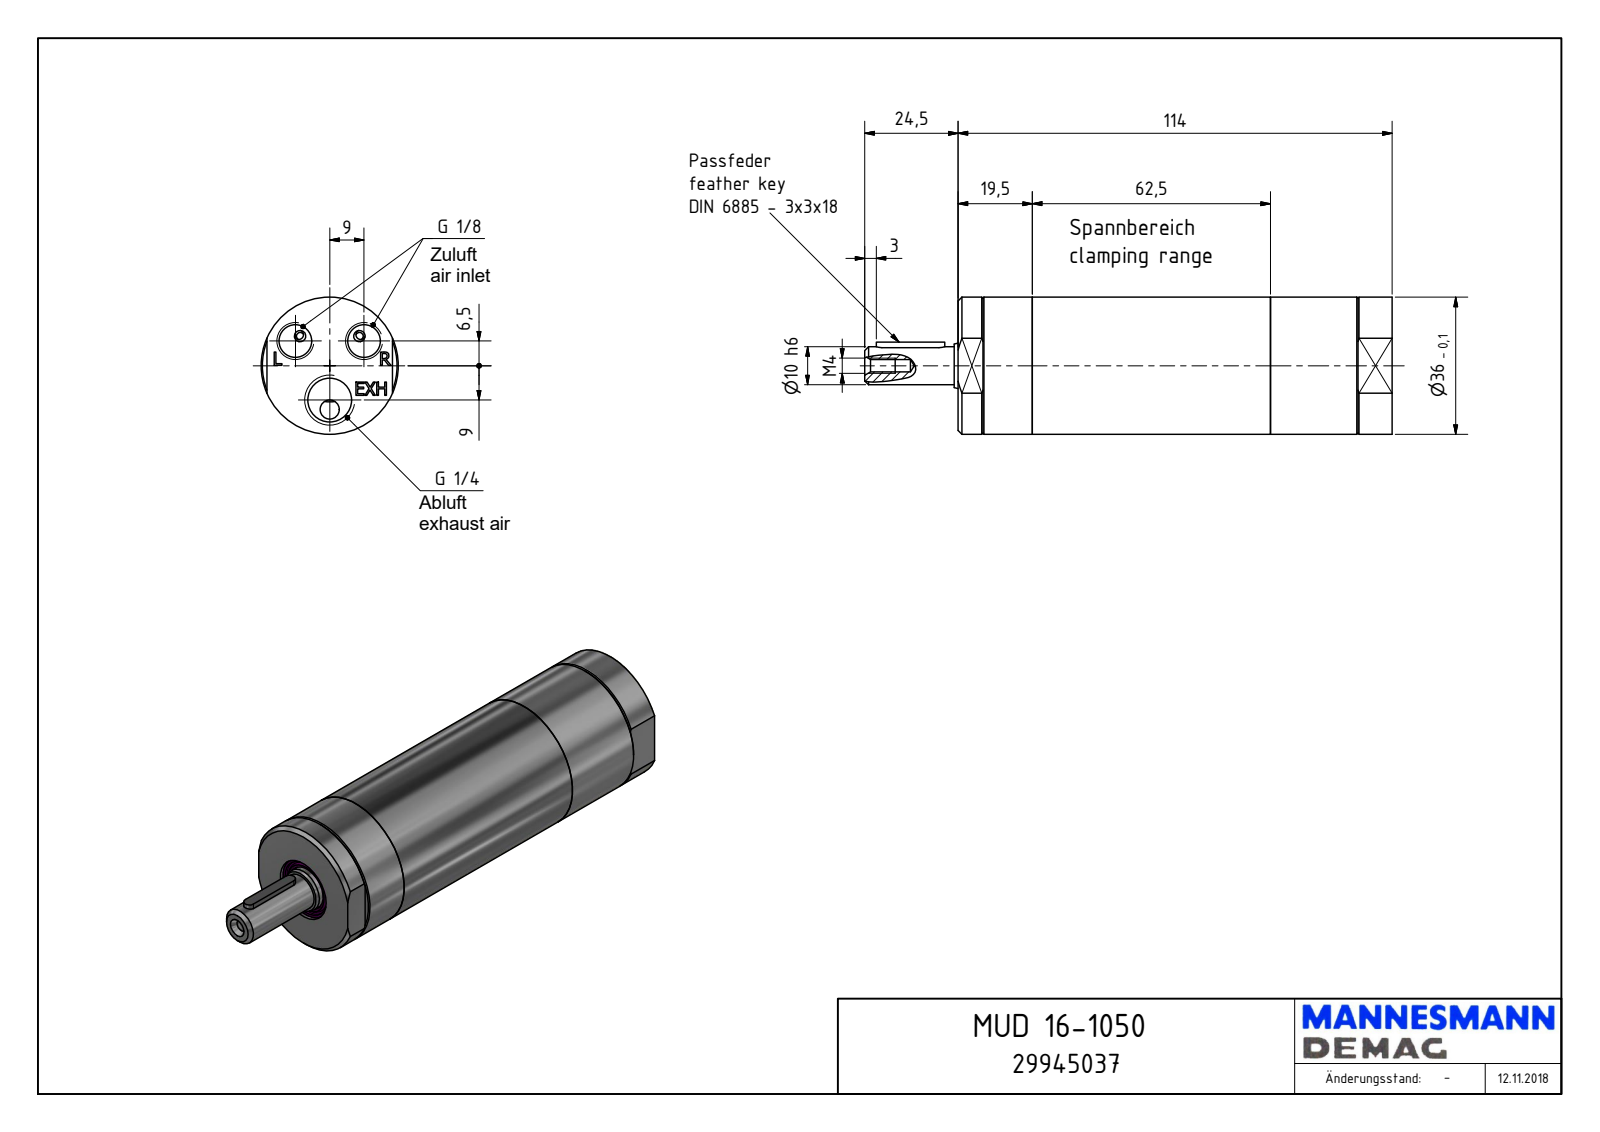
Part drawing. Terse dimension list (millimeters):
name: MUD 16-1050_29945037
written by: Autodesk Inventor 2018 (AUTOMOTIVE_DESIGN)
unit: mm
bodies: 1 solid, 122 faces (79 planar, 17 cylindrical, 26 other)
size: 138.5 × 36 × 36
volume: 115 067 mm³; area: 16 982 mm²
holes: 2× ⌀8.57, 1× ⌀3.24, 1× ⌀11.45, 1× ⌀15.5, 1× ⌀17
bosses: 1× ⌀36, 1× ⌀11.95, 1× ⌀10
rounds: 2× R1.5
face distances: 114, 33, 104.1, 9.9, 1, 15, 18, 103.1, 113, 24.5
hole spacings: 11.1, 17.92, 9, 18
